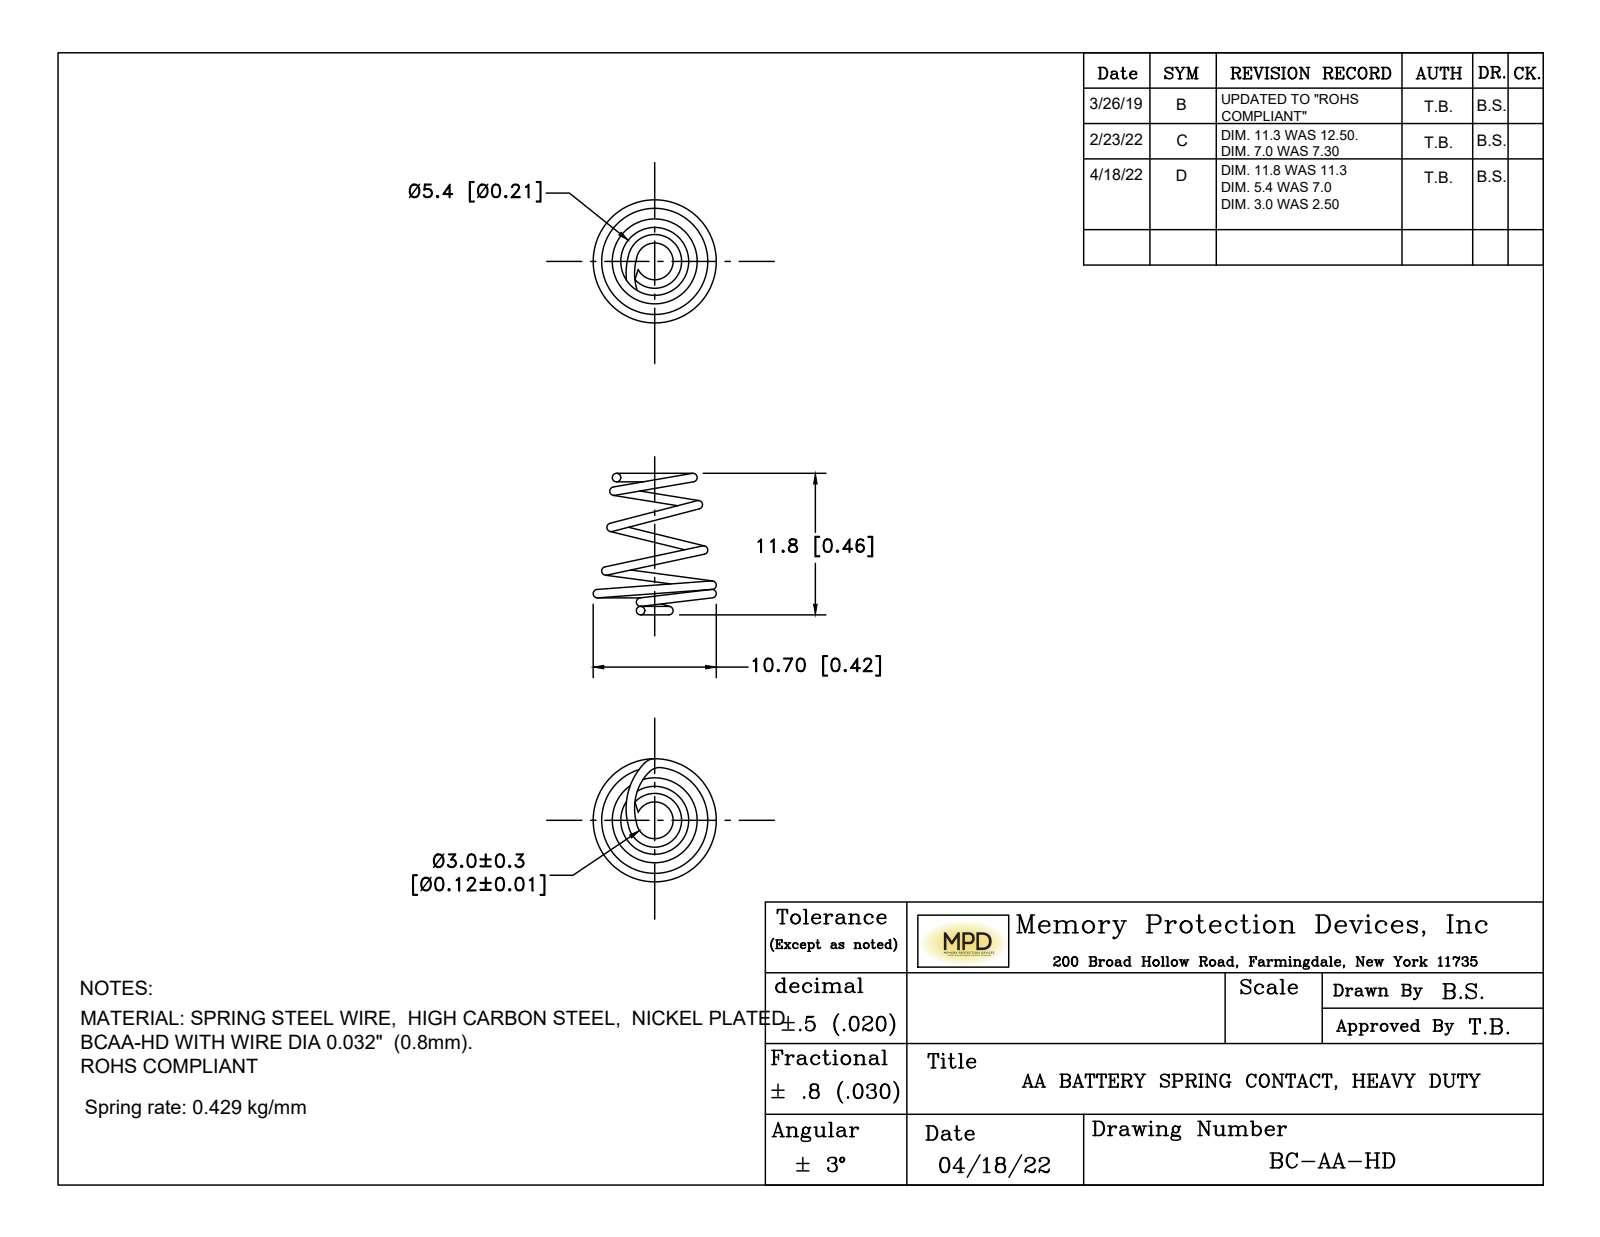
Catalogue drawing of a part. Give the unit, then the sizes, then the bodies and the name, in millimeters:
Units: millimetres
Overall size (bounding box): 12.51 × 10.7 × 10.7
Volume: 64 mm³ · Surface area: 324 mm²
Bodies: 1 solid, 11 faces (3 planar, 0 cylindrical, 8 other)
Part name (STEP PRODUCT): BCAA-HD
STEP written by: SolidWorks 2017 (AUTOMOTIVE_DESIGN)
